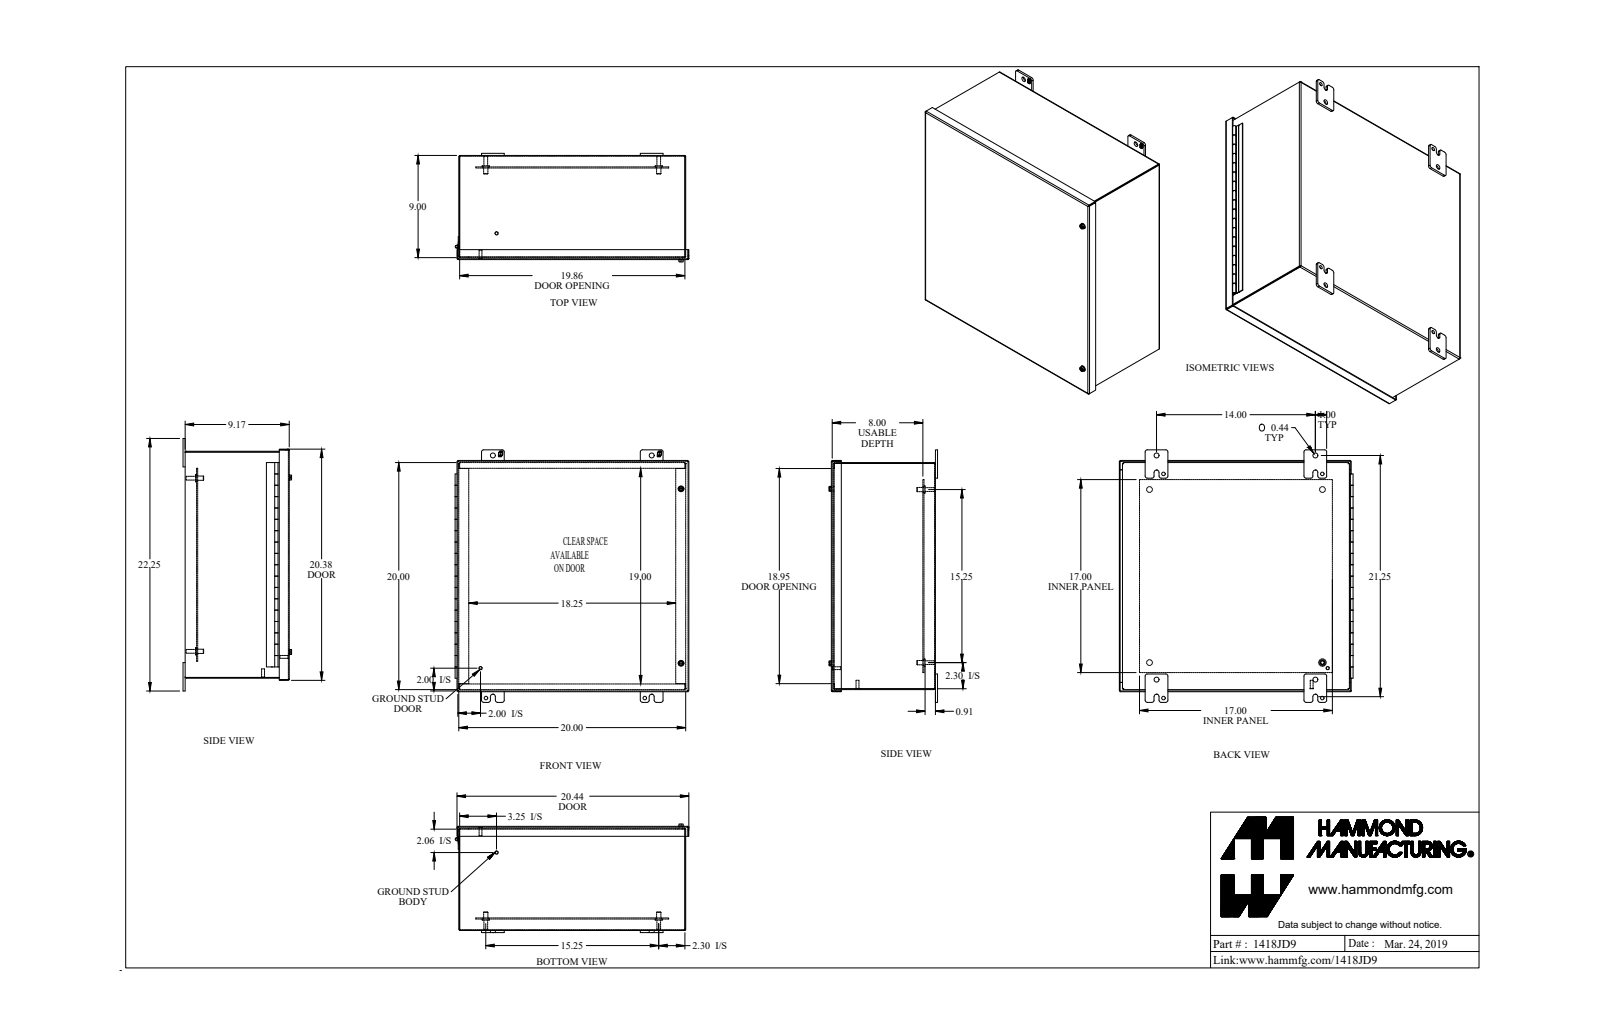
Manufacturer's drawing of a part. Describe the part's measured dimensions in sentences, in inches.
The part is named "1418JD9_Default". Its 3-D file was written by "SolidWorks 2018 (CONFIG_CONTROL_DESIGN)". It is 32 solids with 880 faces: 545 planar, 293 cylindrical and 42 other. Overall it measures 22.25 by 20.604 by 9.571 inches. Its volume is 174.8 cubic inches and its surface area 4 320 square inches. Round holes: 6 of diameter 0.313, 4 of diameter 0.437, 4 of diameter 0.5, 2 of diameter 0.26, 2 of diameter 0.266, 2 of diameter 0.28, 2 of diameter 0.29, 2 of diameter 0.307, 2 of diameter 0.397, 2 of diameter 0.445, 1 of diameter 0.187, 1 of diameter 3.5. Round bosses or shafts: 4 of diameter 0.65, 4 of diameter 0.375, 4 of diameter 0.33, 2 of diameter 1, 2 of diameter 0.51, 2 of diameter 0.5, 2 of diameter 0.39, 2 of diameter 0.281. Partial cylindrical surfaces (rounded edges, fillets, slot ends): 24 of radius 0.188, 20 of radius 0.25, 12 of radius 0.036, 12 of radius 0.108, 8 of radius 0.218, 6 of radius 0.133, 5 of radius 0.06, 4 of radius 0.5. The main face-to-face distances are 0.072, 9.1, 19.928, 9.172, 9.028, 19.856, 20, 8.091, 1.104, 1.032. The hole center spacings are 15.25, 1.736, 14, 19.75, 21.567, 24.209, 1.907, 1.966.
